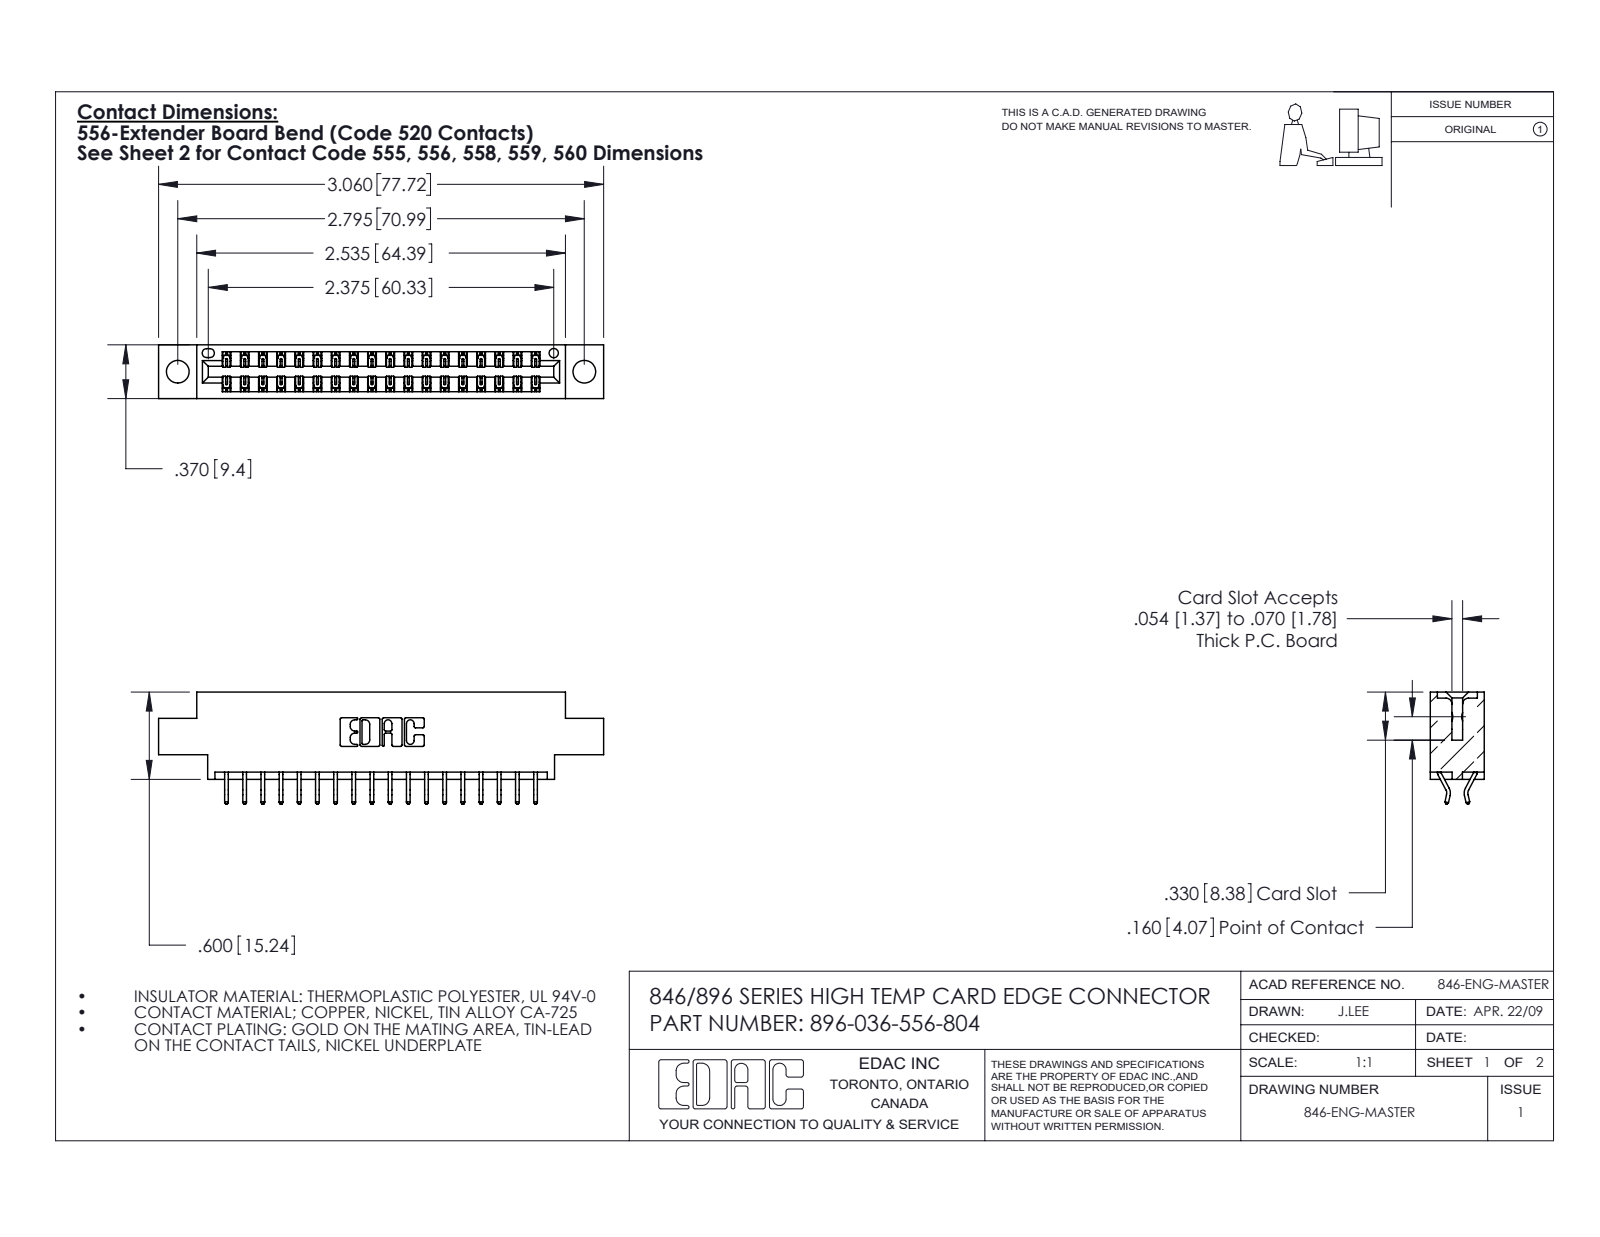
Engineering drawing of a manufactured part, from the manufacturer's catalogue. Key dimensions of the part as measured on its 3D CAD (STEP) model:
Part name (STEP PRODUCT): 345-292-001_556 Tail; 346 Part_0.170 Offset - 0.156 Dia-TH; 396-036-556-804
STEP written by: SolidWorks 2016 (CONFIG_CONTROL_DESIGN)
Units: inches
Bodies: 37 solids, 2214 faces (1484 planar, 730 cylindrical, 0 other)
Overall size (bounding box): 3.06 × 0.77 × 0.37
Volume: 0.436 in³ · Surface area: 14.58 in²
Round holes (diameter × count): ⌀0.156 ×2, ⌀0.064 ×1
Partial cylindrical surfaces — rounded edges, fillets, slot ends (radius × count): R0.006 ×54, R0.01 ×22, R0.007 ×6, R0.031 ×6, R0.026 ×3, R0.01 ×2, R0.014 ×2, R0.022 ×2
Main face-to-face distances: 0.048, 0.322, 0.37, 0.25, 0.025, 0.072, 0.298, 0.275, 0.148, 0.222
Hole centre spacings: 0.246, 2.588, 2.795
